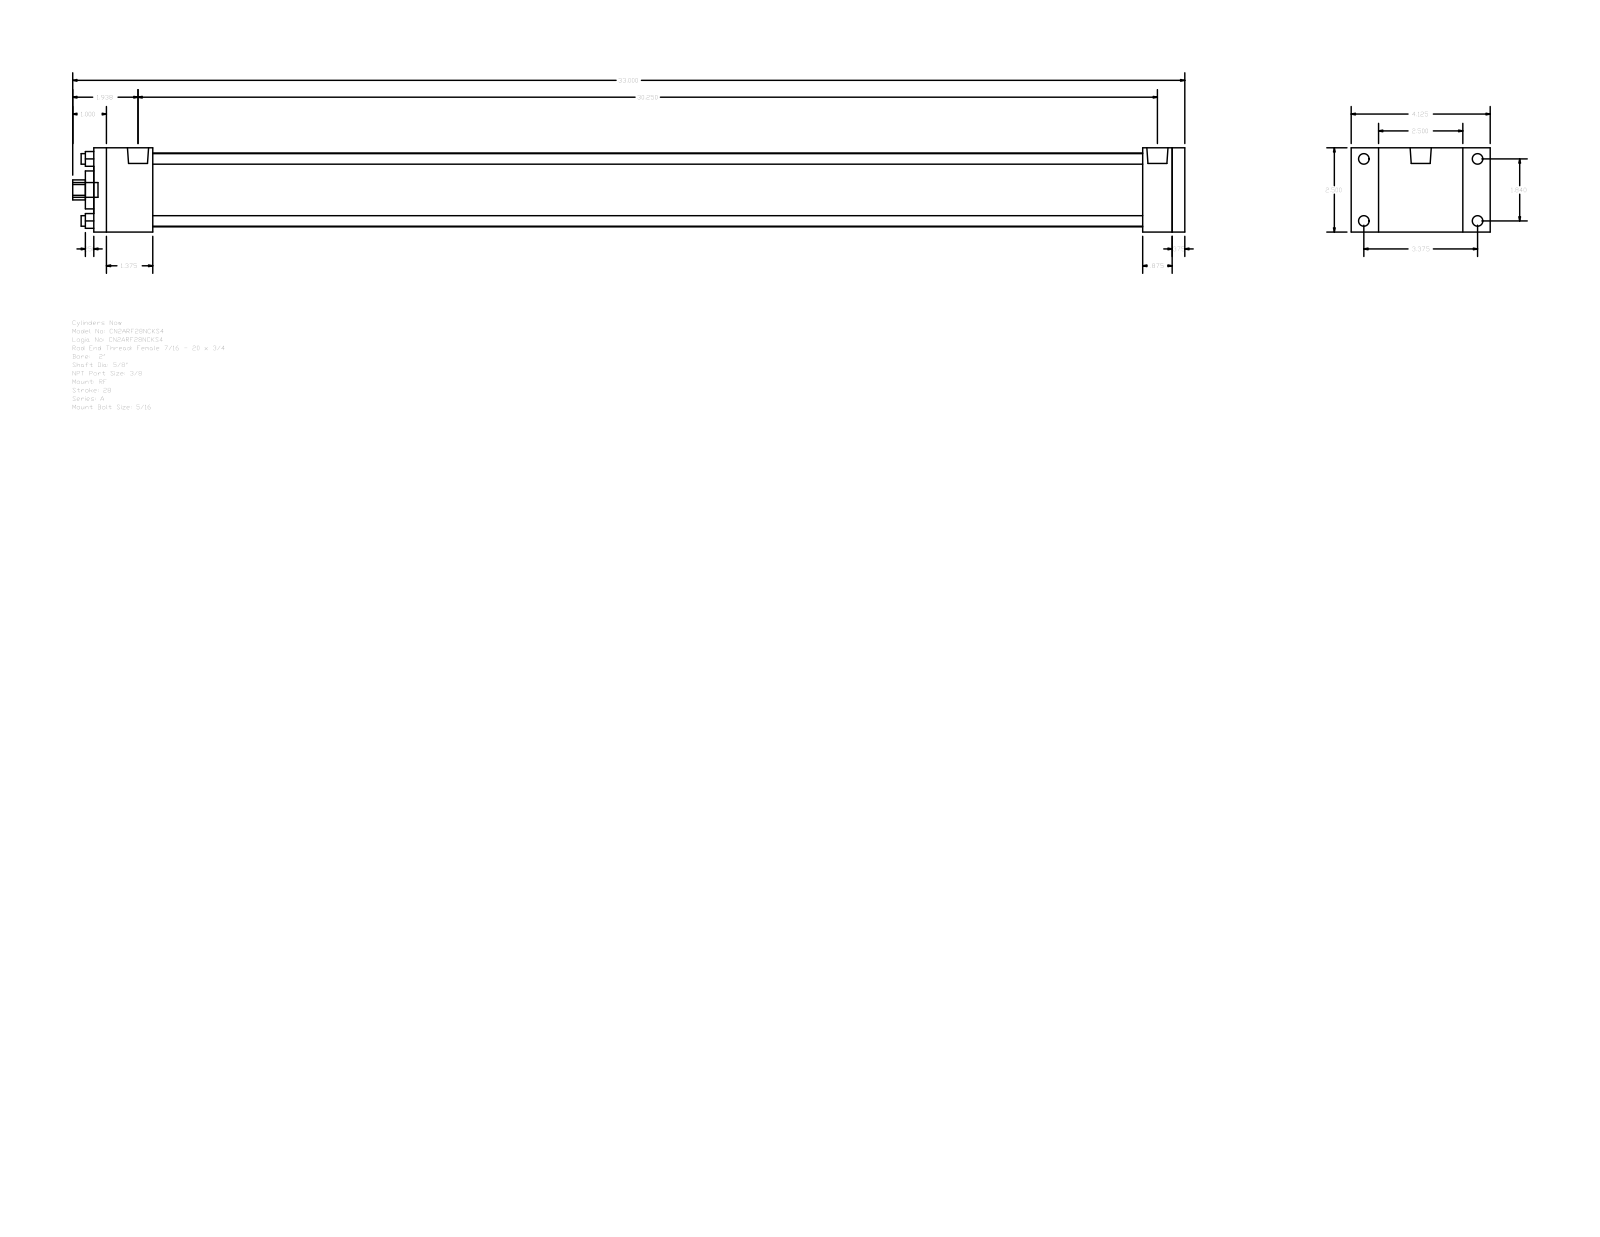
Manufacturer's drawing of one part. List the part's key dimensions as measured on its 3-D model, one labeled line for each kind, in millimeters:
Part name (STEP PRODUCT): A_RF__0200_0.625
STEP written by: GSSL Pune (CONFIG_CONTROL_DESIGN)
Units: millimetres
Bodies: 0 solids, 92 faces (64 planar, 28 cylindrical, 0 other)
Overall size (bounding box): 838.2 × 104.78 × 63.5
Round holes (diameter × count): ⌀7.94 ×4, ⌀15.88 ×1, ⌀28.57 ×1, ⌀55.63 ×1
Round bosses / shafts (diameter × count): ⌀7.94 ×4, ⌀5.56 ×4, ⌀15.93 ×2, ⌀11.11 ×1
Partial cylindrical surfaces — rounded edges, fillets, slot ends (radius × count): R7.54 ×1
Main face-to-face distances: 63.5, 822.32, 9.53, 812.79, 44.45, 768.34, 777.87, 790.57, 746.12, 22.22
Hole centre spacings: 33.05, 46.74, 66.1
